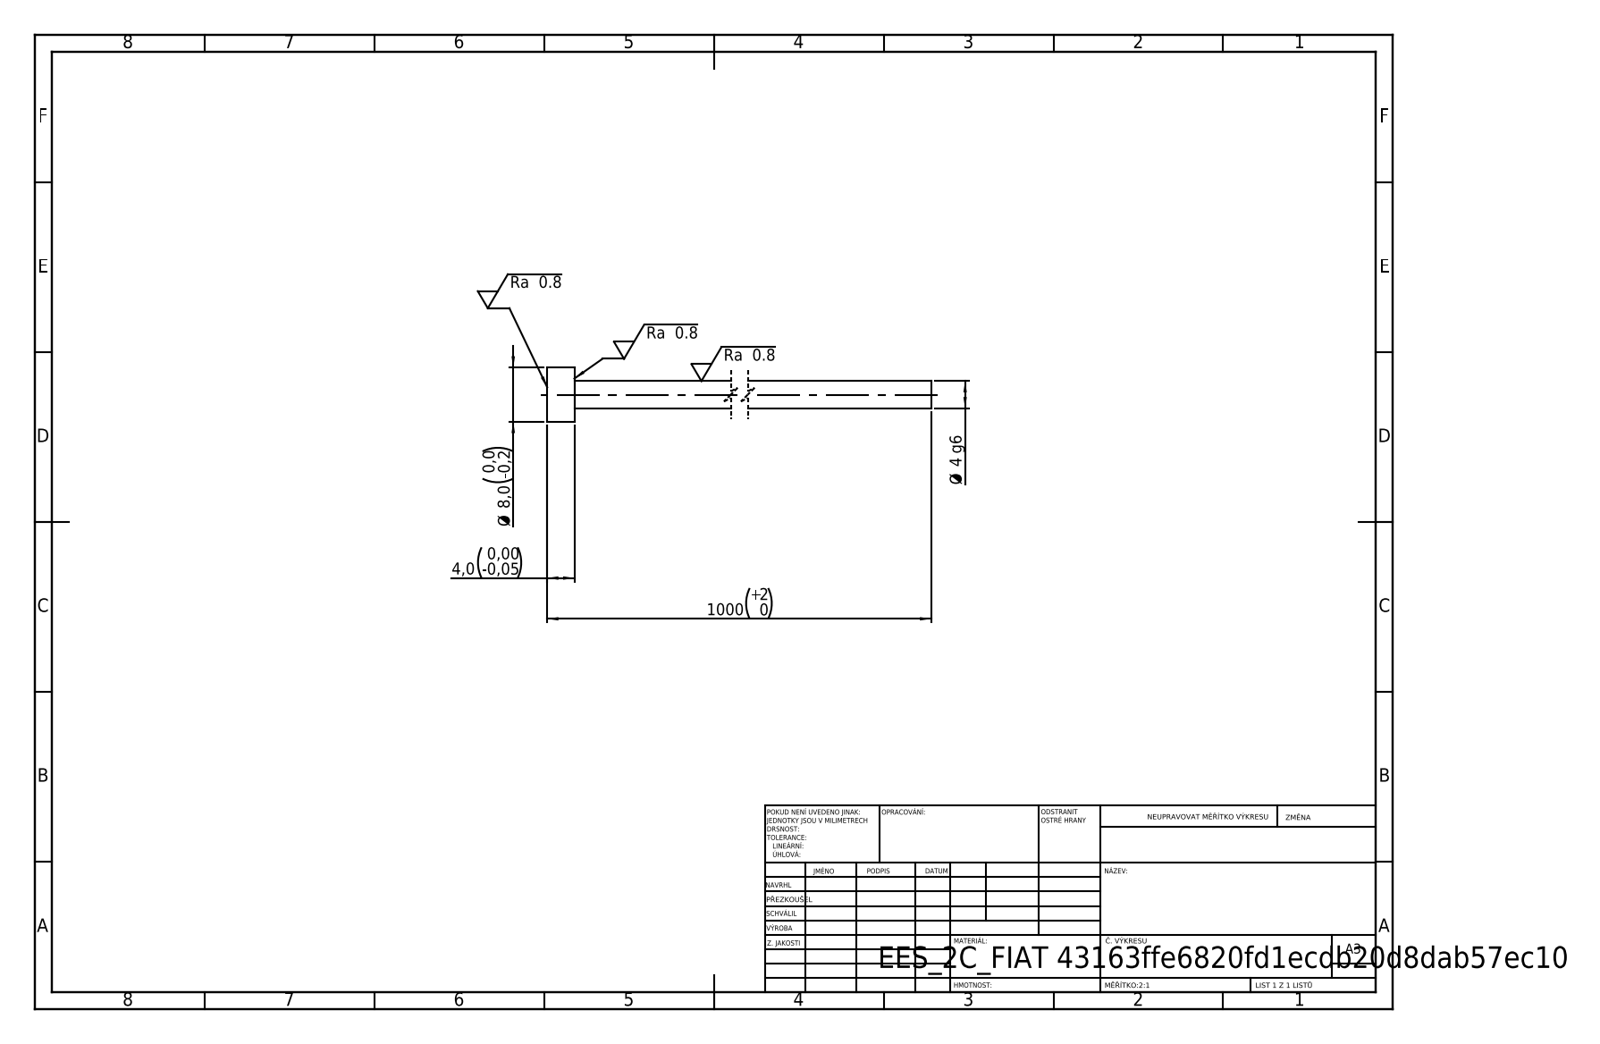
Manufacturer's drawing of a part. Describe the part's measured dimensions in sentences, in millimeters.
Its 3-D file was written by "SolidWorks 2019 (CONFIG_CONTROL_DESIGN)". It is 1 solid with 7 faces: 3 planar, 4 cylindrical and 0 other. Overall it measures 1000 by 8 by 8 millimeters. Its volume is 12 717 cubic millimeters and its surface area 12 717 square millimeters. Round bosses or shafts: 1 of diameter 8, 1 of diameter 4. The main face-to-face distances are 4, 1000, 996.
